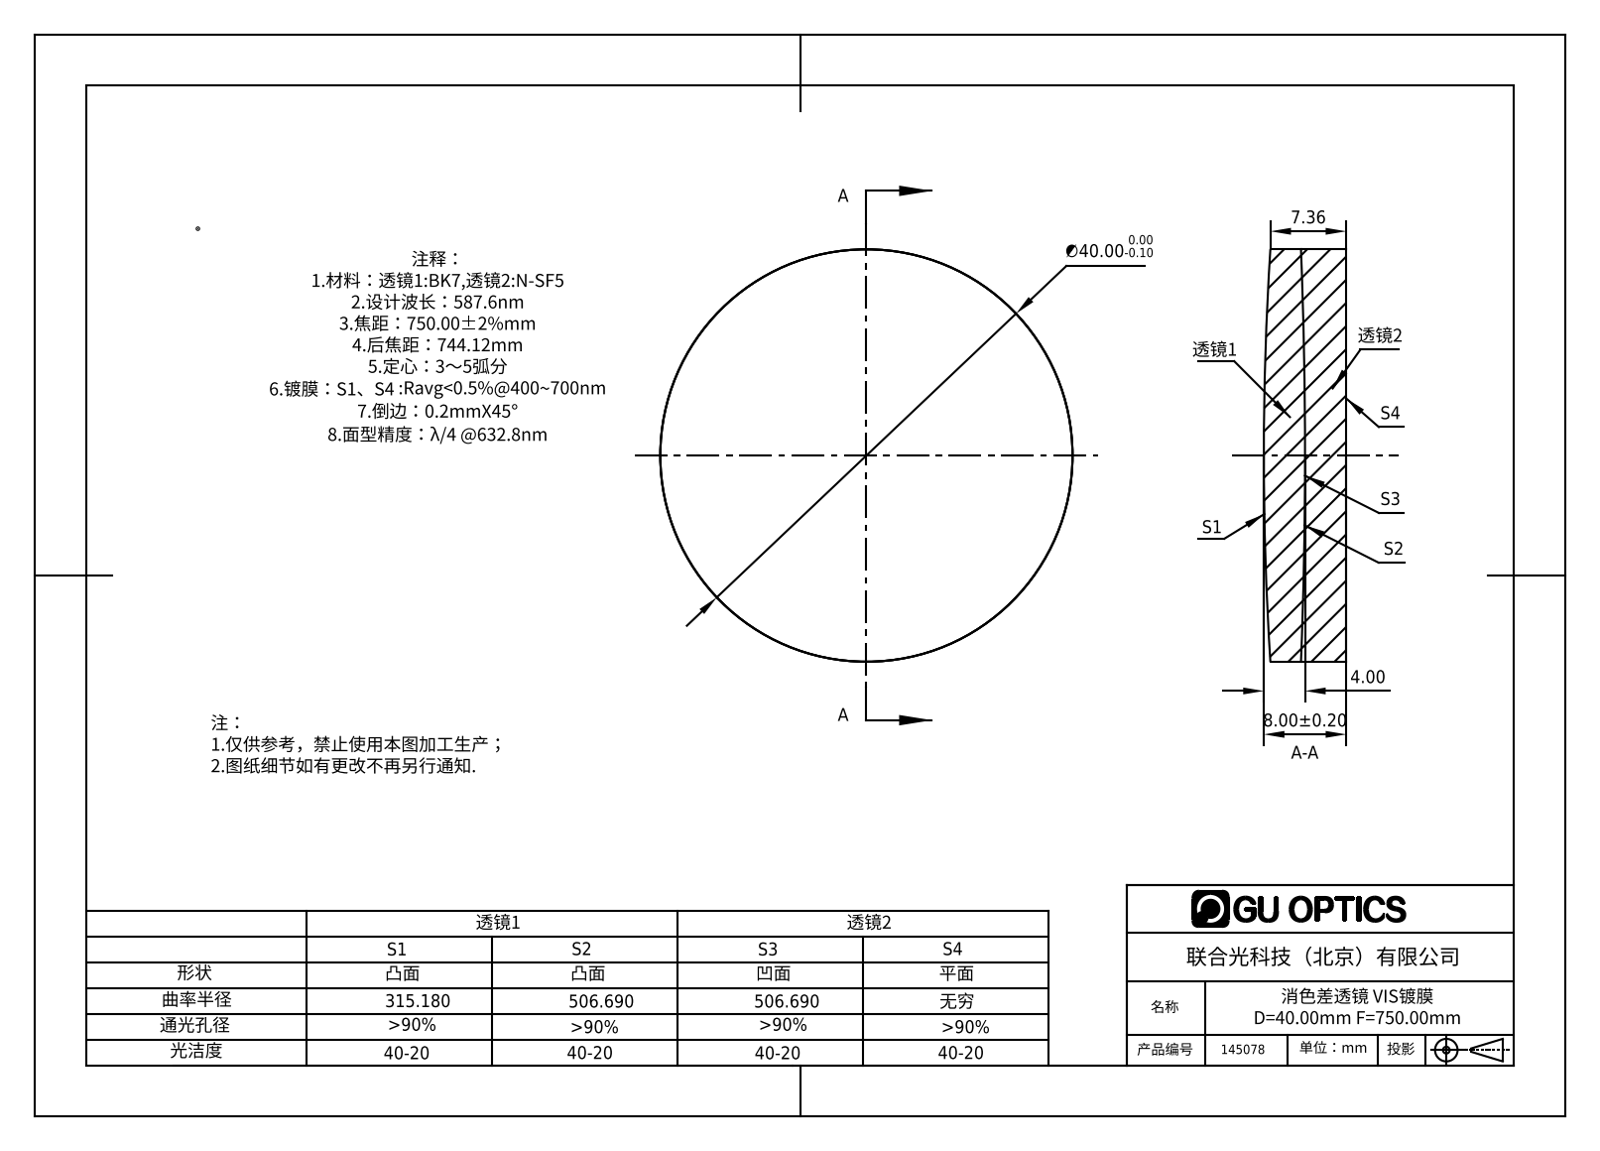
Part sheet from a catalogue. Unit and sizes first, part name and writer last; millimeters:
Units: millimetres
Overall size (bounding box): 40 × 40 × 8
Round bosses / shafts (diameter × count): ⌀40 ×1
Volume: 9 654 mm³ · Surface area: 5 954 mm²
Bodies: 2 solids, 11 faces (1 planar, 4 cylindrical, 6 other)
Part name (STEP PRODUCT): 145078
STEP written by: SolidWorks 2016 (AUTOMOTIVE_DESIGN)
